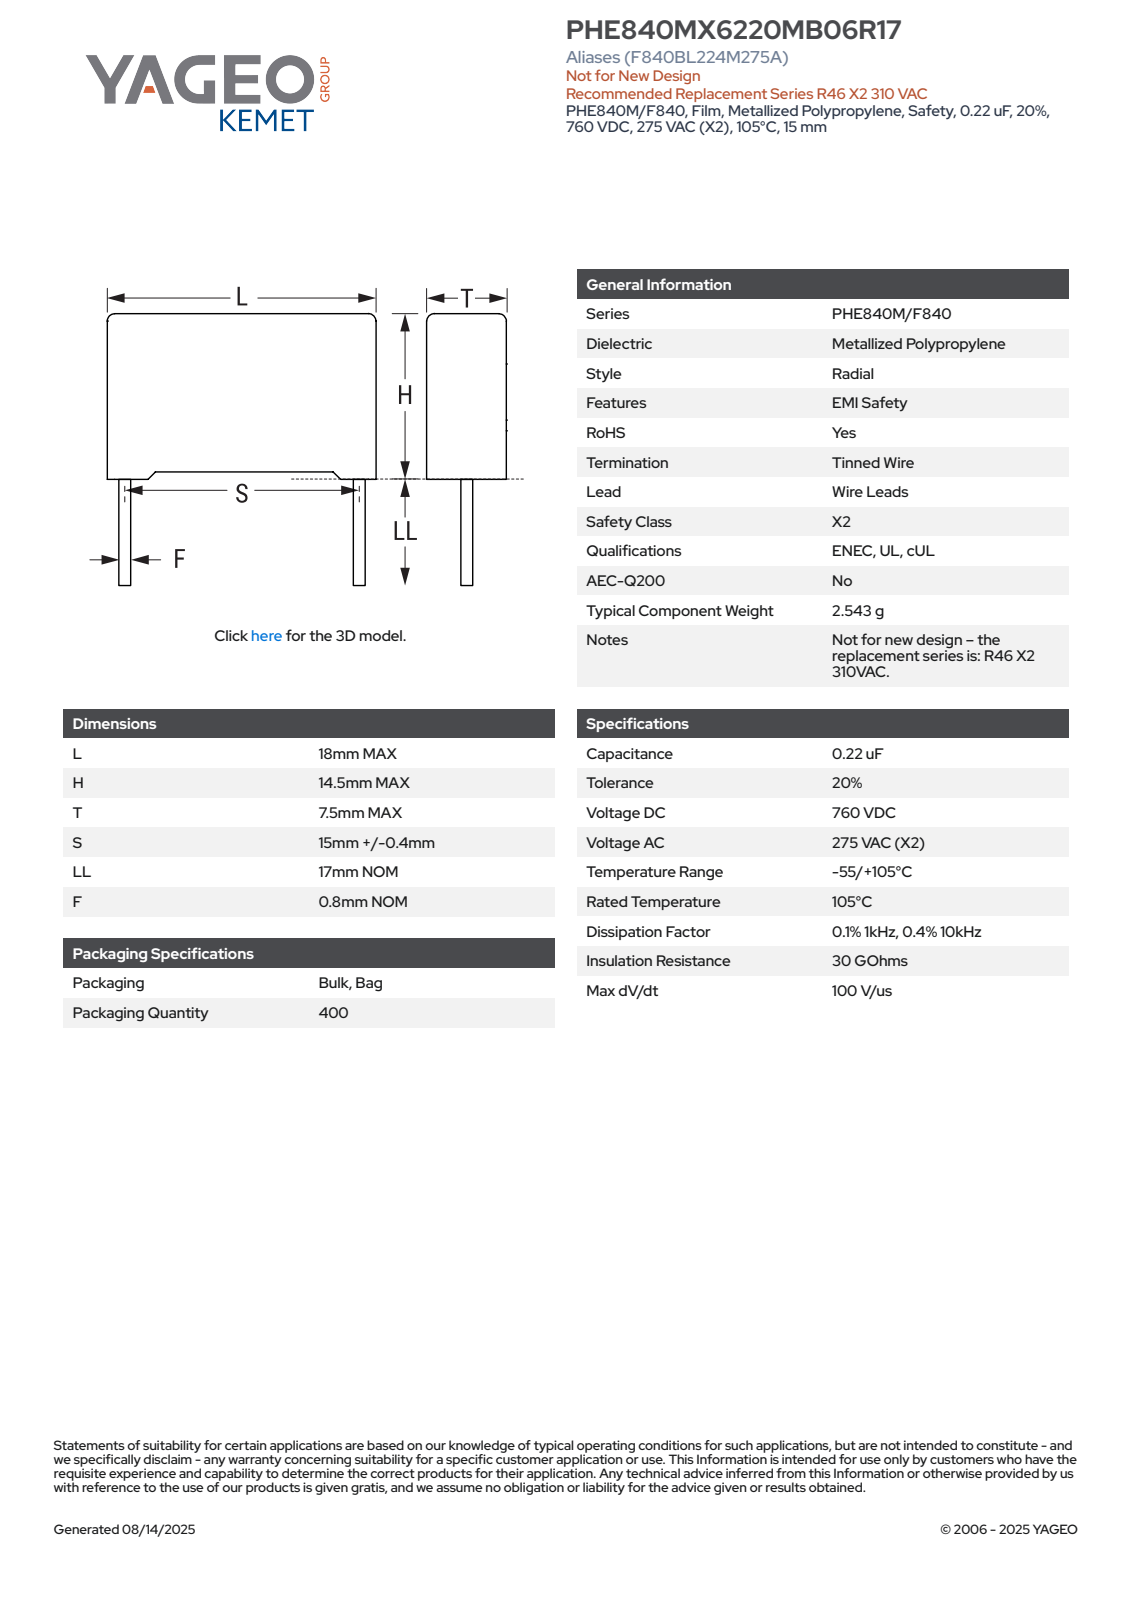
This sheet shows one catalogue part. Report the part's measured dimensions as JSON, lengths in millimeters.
{"part_name": "CFR_RB2_18X14.5X7.5_L18H14.5T7.5S15LL17F0.8", "step_written_by": "SolidWorks 2021 (AUTOMOTIVE_DESIGN)", "units": "millimeters", "bodies": {"solids": 4, "faces": 85, "planar": 77, "cylindrical": 8, "other": 0}, "overall_size": [31.5, 18, 7.5], "volume_mm3": 1886, "surface_area_mm2": 1124, "round_bosses_or_shafts": [[0.8, 2]], "partial_cylinders_radius": [[0.5, 4]], "face_to_face_distances": [7.5, 18, 13.75, 0.6, 0.75, 14.5, 6.9, 0.5, 14, 17.4]}
